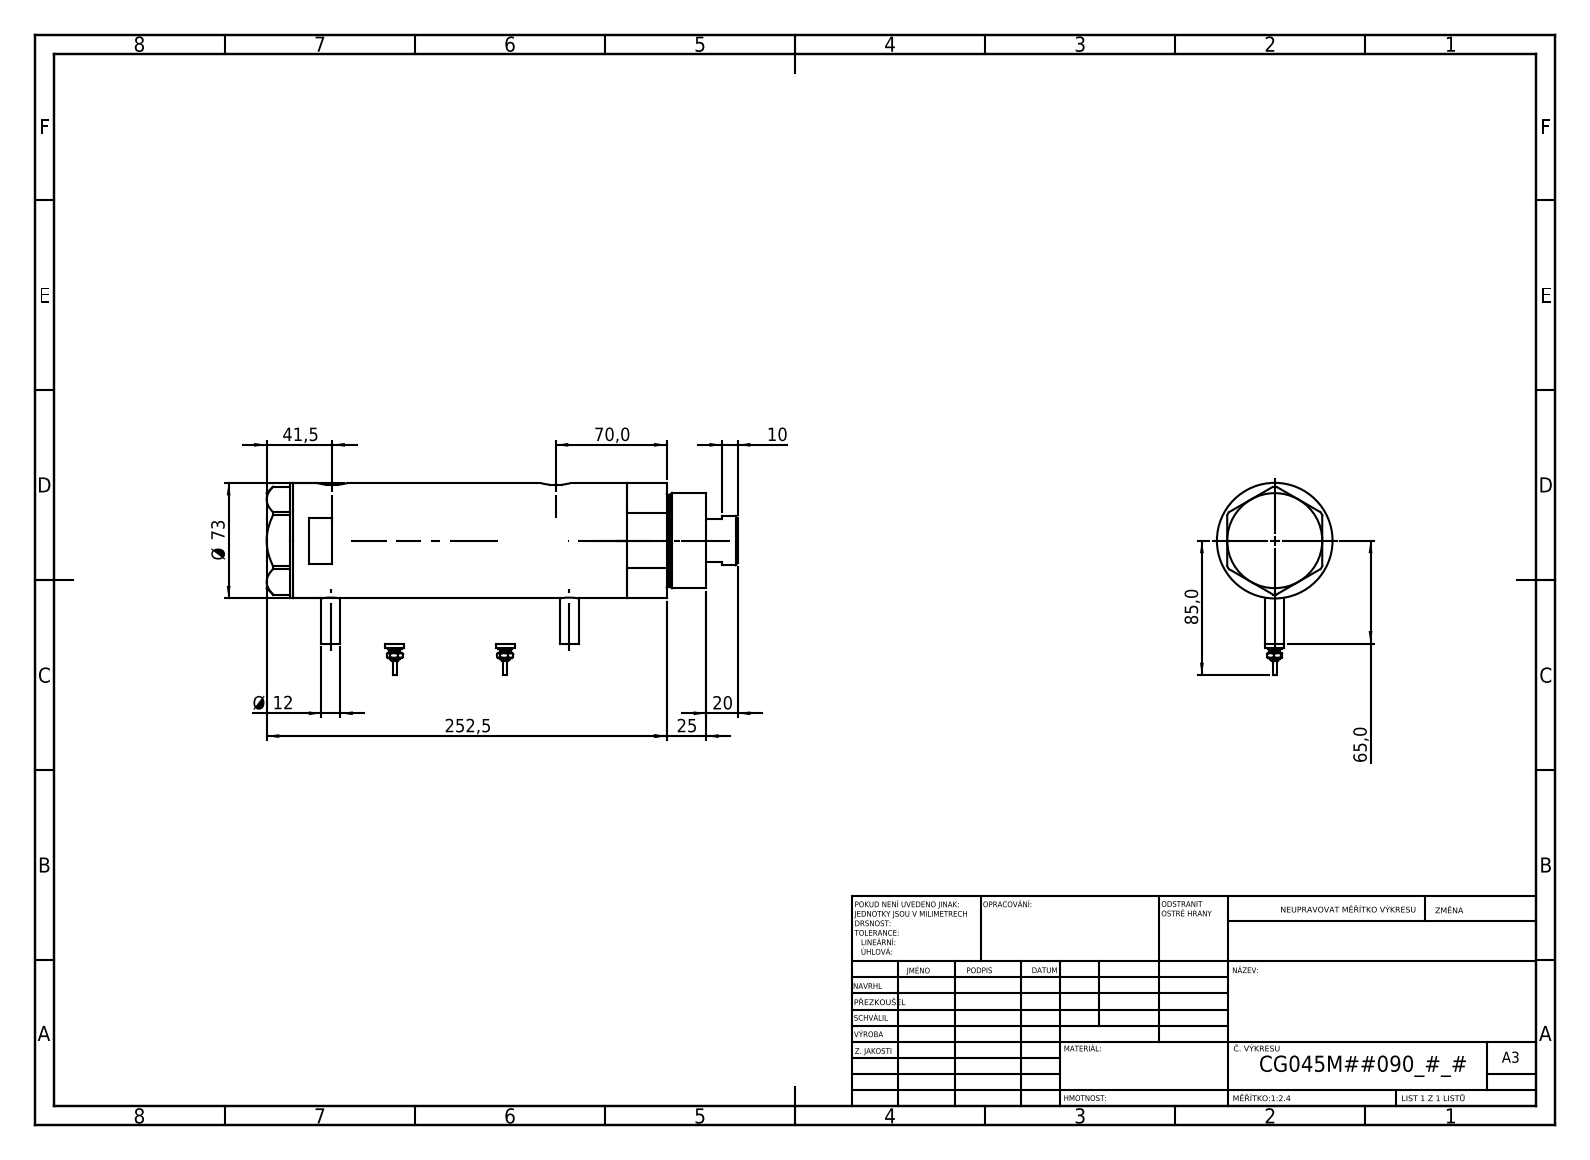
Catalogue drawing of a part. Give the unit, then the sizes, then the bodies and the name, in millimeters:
Units: millimetres
Overall size (bounding box): 297.5 × 121.5 × 73
Round holes (diameter × count): ⌀12.5 ×2, ⌀13.16 ×2, ⌀10.5 ×1, ⌀32 ×1, ⌀33.5 ×1, ⌀45 ×1, ⌀48 ×1, ⌀64 ×1
Round bosses / shafts (diameter × count): ⌀12 ×4, ⌀9 ×2, ⌀7 ×2, ⌀4.5 ×2, ⌀2.5 ×2, ⌀73 ×1, ⌀60 ×1, ⌀58 ×1
Partial cylindrical surfaces — rounded edges, fillets, slot ends (radius × count): R10 ×2
Main face-to-face distances: 166, 26, 140, 16.5, 42.5, 182.5, 2, 261, 277.5, 235
Hole centre spacings: 1, 8.5, 141, 142, 149.5, 150.5
Volume: 1 049 000 mm³ · Surface area: 173 139 mm²
Bodies: 6 solids, 212 faces (77 planar, 71 cylindrical, 64 other)
Part name (STEP PRODUCT): V270CG_MIDDLE; V270CG_FRONT; V270CG_VC; Switch (+1 more)
STEP written by: SolidWorks 2019 (CONFIG_CONTROL_DESIGN)
